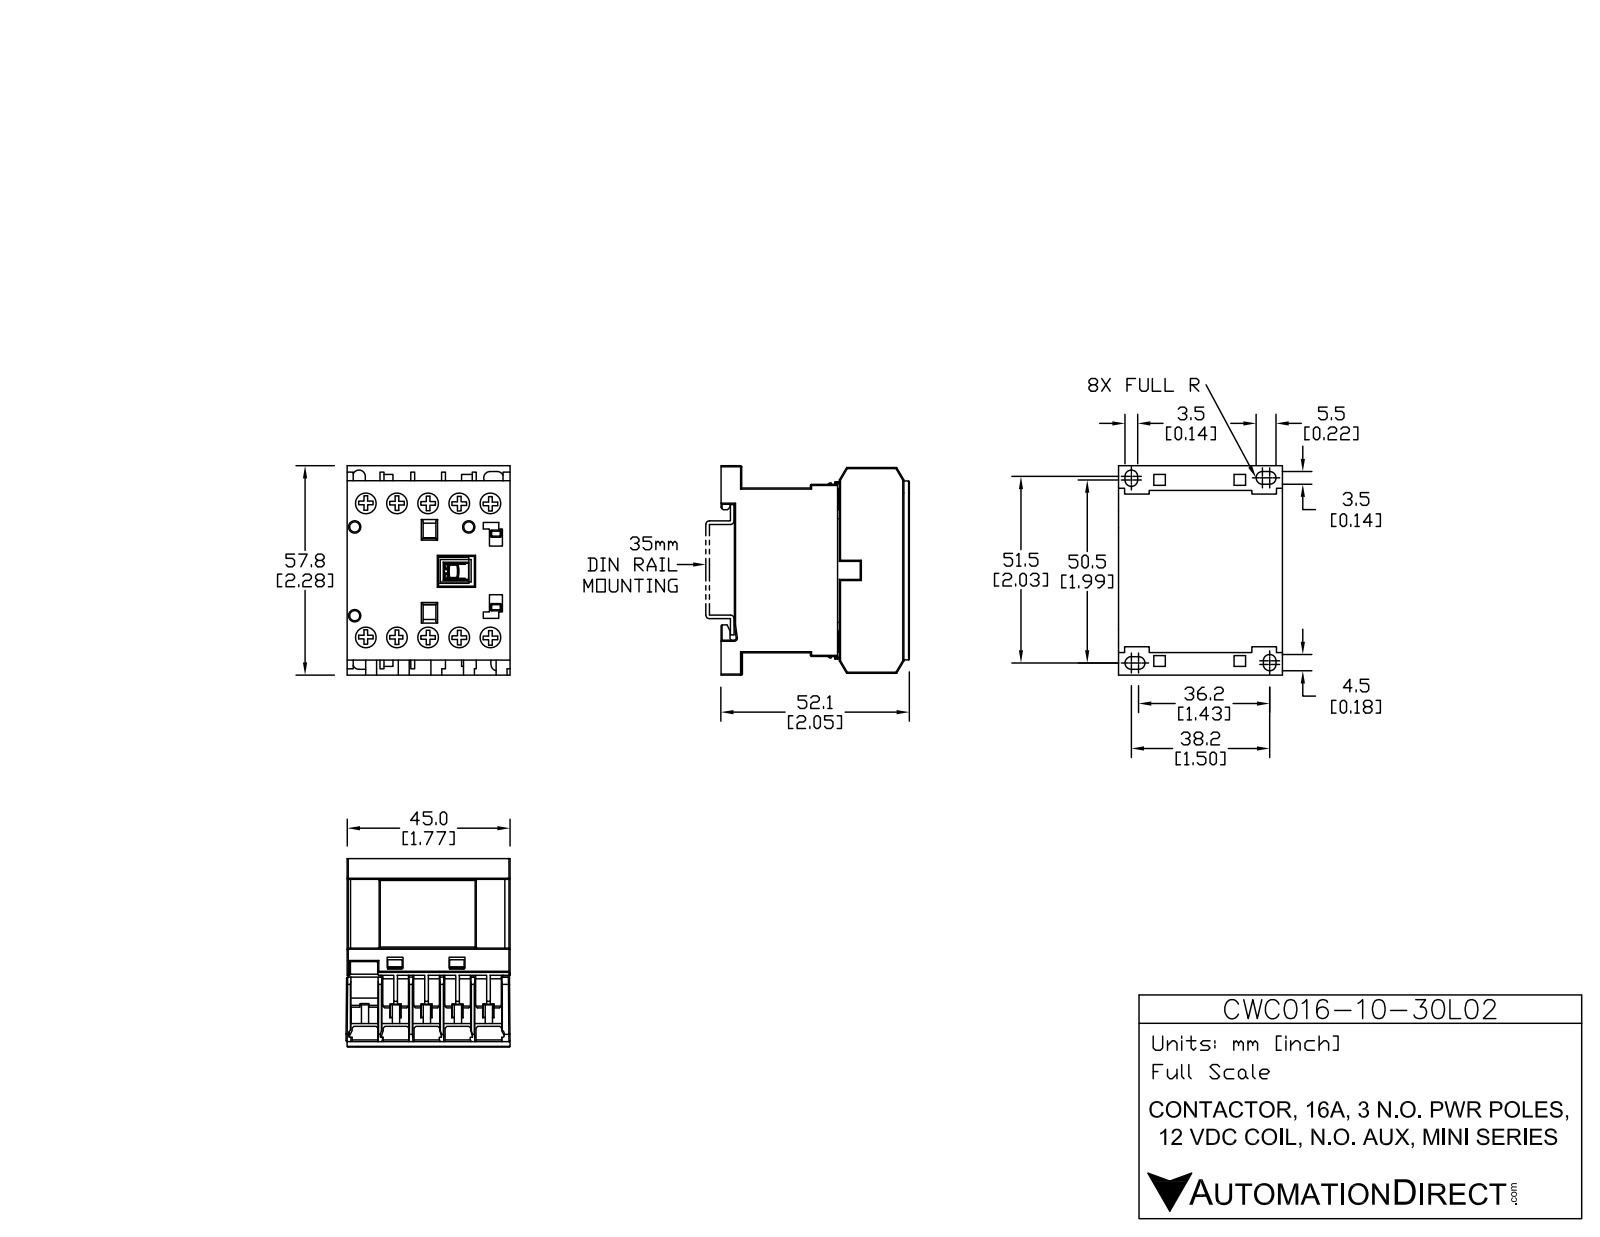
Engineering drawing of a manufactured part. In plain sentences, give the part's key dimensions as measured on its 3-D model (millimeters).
The part is named "CWC16-10-30L02". Its 3-D file was written by "SolidWorks 2013 (AUTOMOTIVE_DESIGN)". It is 15 solids with 535 faces: 445 planar, 90 cylindrical and 0 other. Overall it measures 58.04 by 52.12 by 45.75 millimeters. Its volume is 97 133 cubic millimeters and its surface area 30 437 square millimeters. Round holes: 10 of diameter 6.2, 3 of diameter 2.8. Round bosses or shafts: 10 of diameter 5.9. Partial cylindrical surfaces (rounded edges, fillets, slot ends): 20 of radius 0.3, 6 of radius 1.72, 2 of radius 1.73, 1 of radius 0.32, 1 of radius 0.42, 1 of radius 0.55. The main face-to-face distances are 8.25, 45.5, 1.25, 16.5, 9.5, 5.5, 17.75, 5.13, 10.63, 7. The hole center spacings are 8.55, 37.94, 17.1, 40.72, 36.96, 25.65, 44.99, 6.91.
